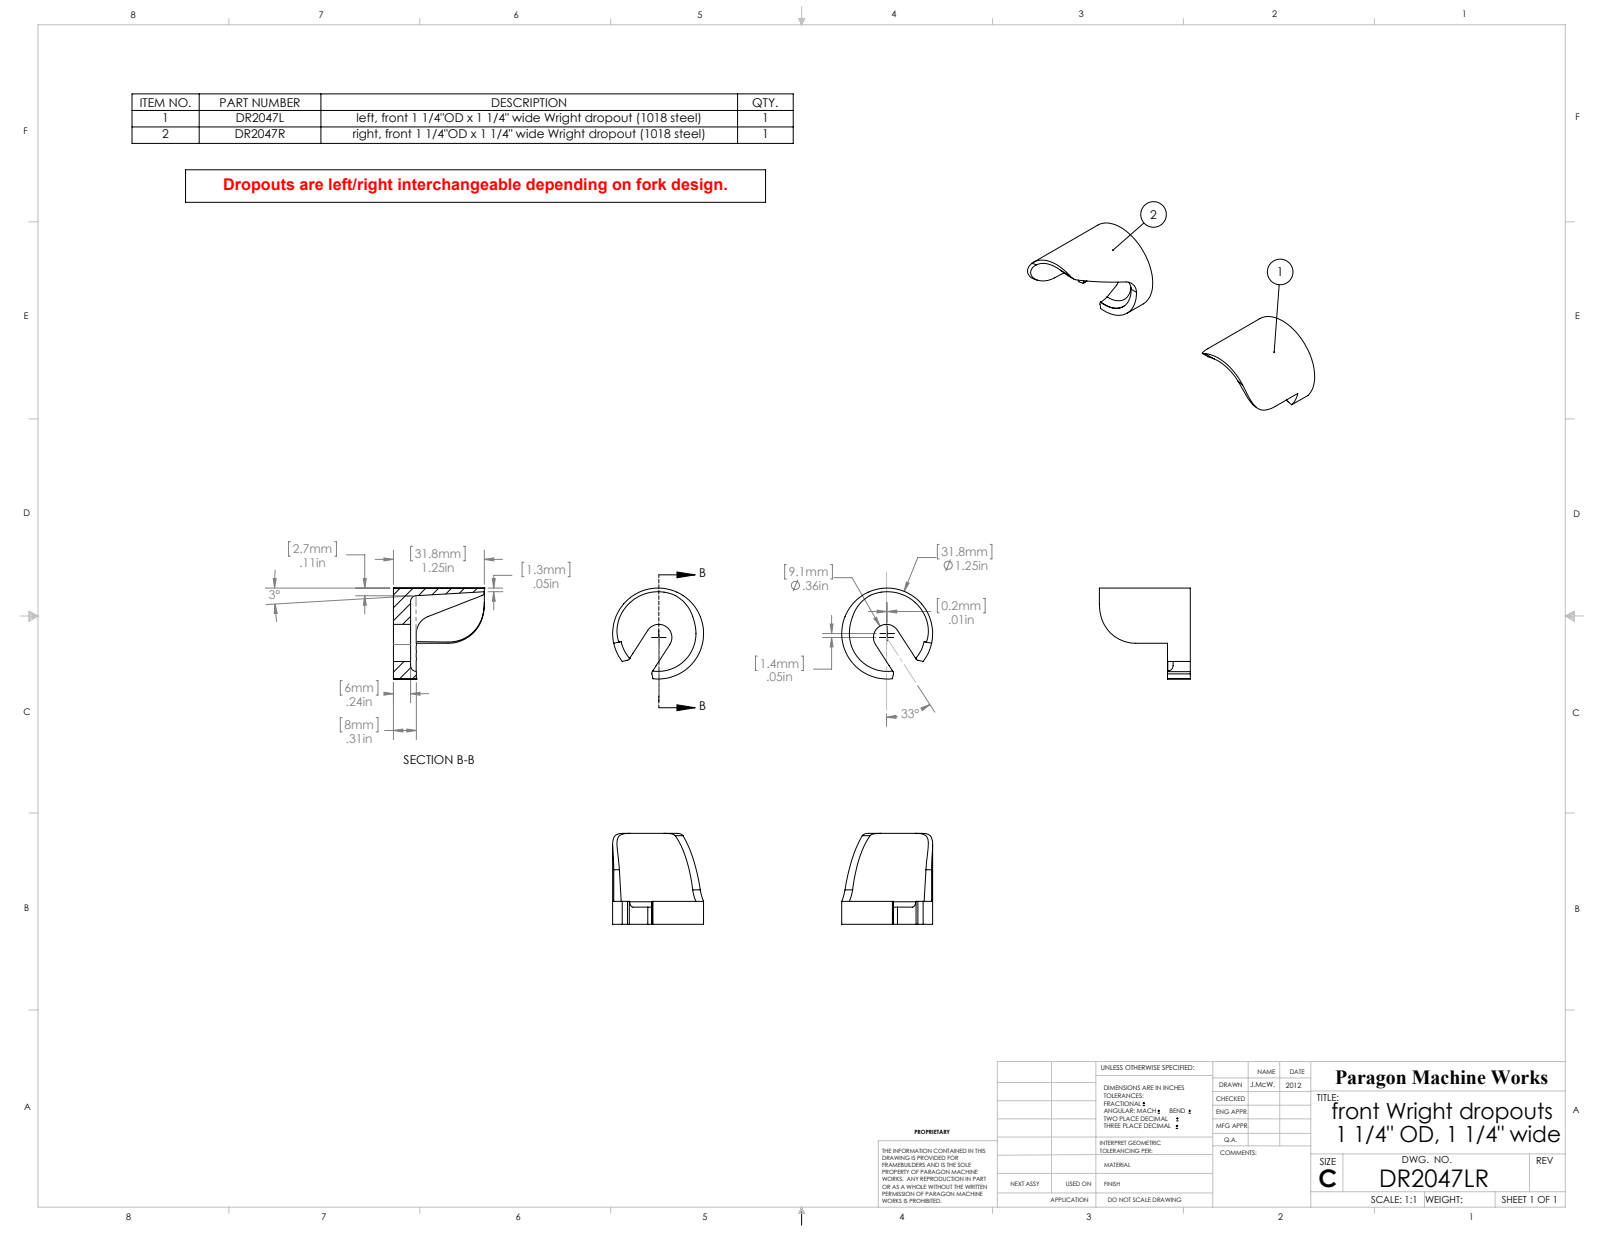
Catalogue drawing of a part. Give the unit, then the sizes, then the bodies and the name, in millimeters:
Units: millimetres
Overall size (bounding box): 111.75 × 31.75 × 31.75
Round bosses / shafts (diameter × count): ⌀31.75 ×2
Partial cylindrical surfaces — rounded edges, fillets, slot ends (radius × count): R1.02 ×4, R4.57 ×2, R12.7 ×2, R1.27 ×1, R6.35 ×1
Main face-to-face distances: 6, 8, 2, 9.15, 31.75, 25.75, 23.75
Volume: 12 153 mm³ · Surface area: 8 318 mm²
Bodies: 2 solids, 40 faces (22 planar, 14 cylindrical, 4 other)
Part name (STEP PRODUCT): DR2047R; DR2047L; DR2047LR
STEP written by: SolidWorks 2012 (AUTOMOTIVE_DESIGN)
